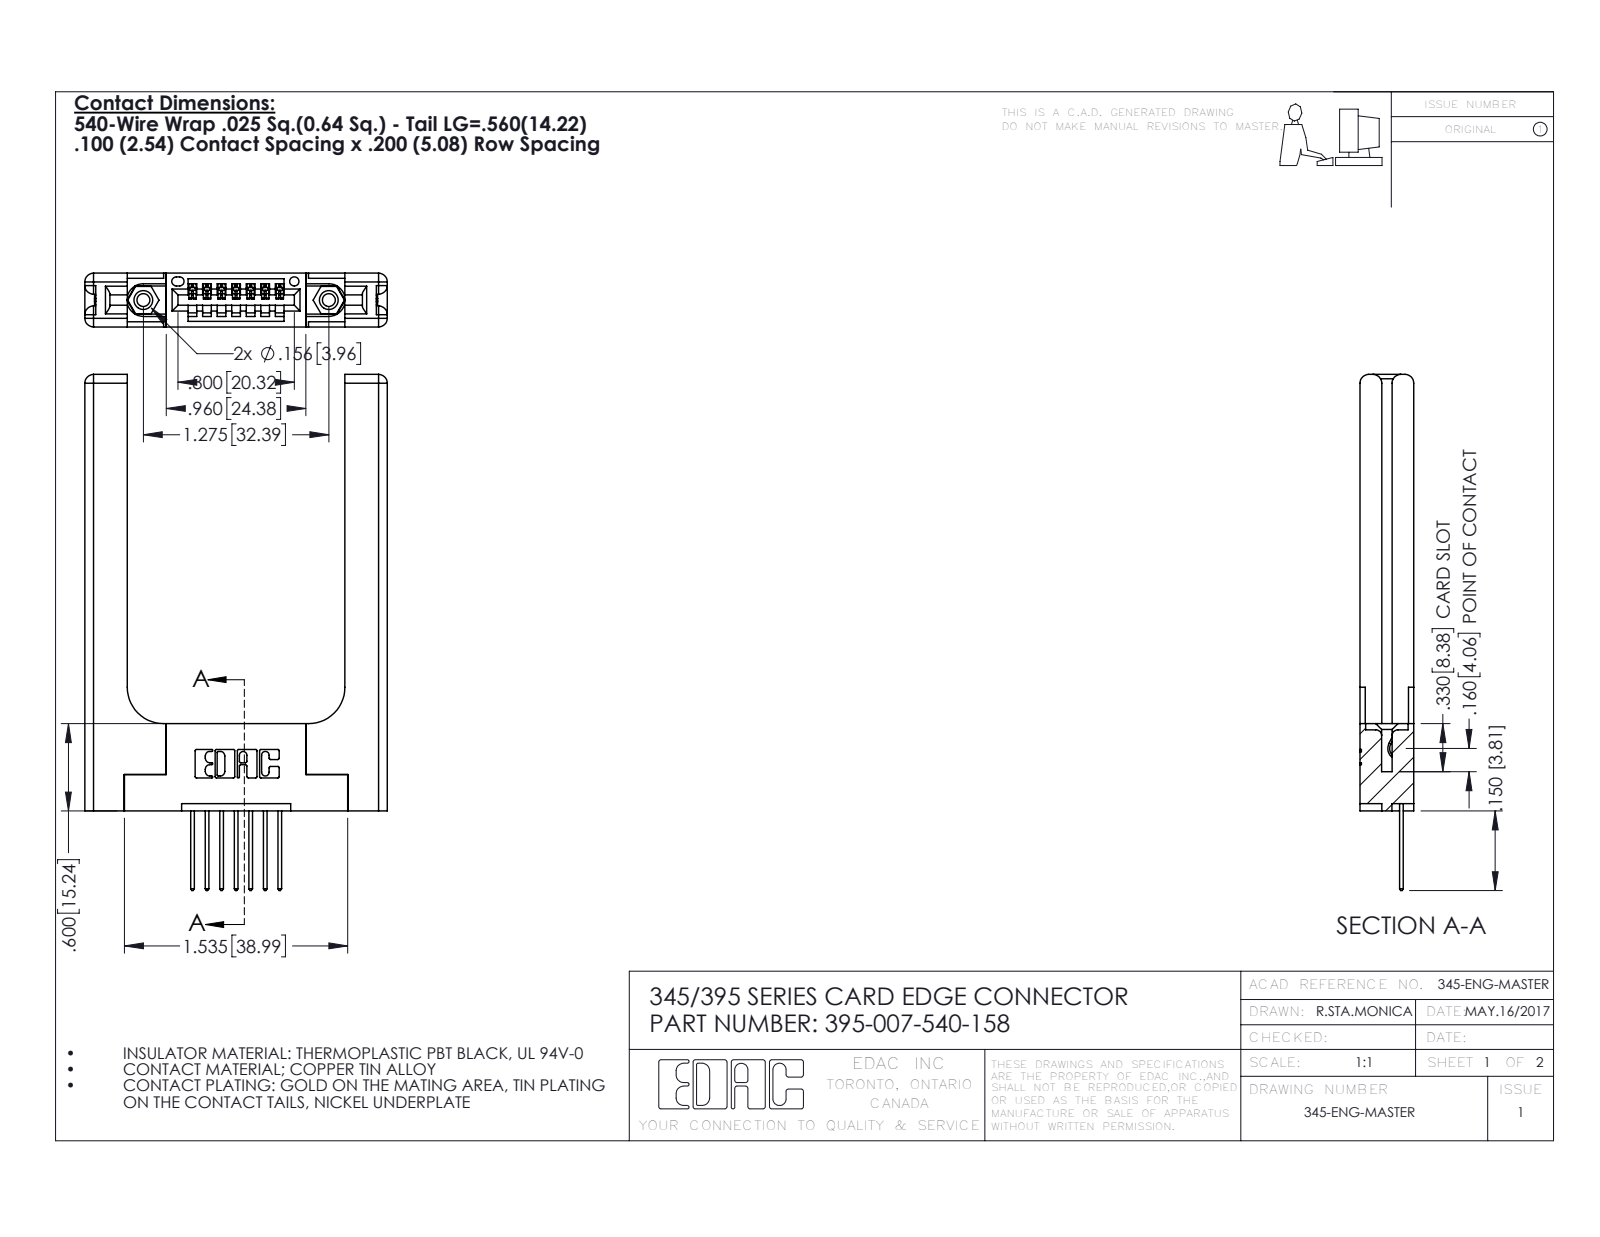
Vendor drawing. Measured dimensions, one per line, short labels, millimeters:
name: 345-250-001_345-250-001-102; 345 Part_Flush Mounting Lugs - 0.156 Dia-TH; 345-220-058_345-220-058; 345-292-001_345-293-140 (+1 more)
written by: SolidWorks 2016 (CONFIG_CONTROL_DESIGN)
unit: mm
bodies: 12 solids, 788 faces (508 planar, 220 cylindrical, 60 other)
size: 90.1 × 52.8 × 9.4
volume: 13 200 mm³; area: 11 190 mm²
holes: 2× ⌀2.3, 2× ⌀3.2, 2× ⌀4, 1× ⌀1.6
bosses: 2× ⌀3.9
rounds: 22× R0.3, 16× R1.5, 14× R0.2, 14× R0.3, 6× R0.2, 6× R0.8, 3× R0.7, 2× R0.8
face distances: 9.4, 3.8, 5.6, 1.8, 2, 3.8, 7.6, 38, 5.1, 1.8
hole spacings: 6.9, 26.5, 32.4
